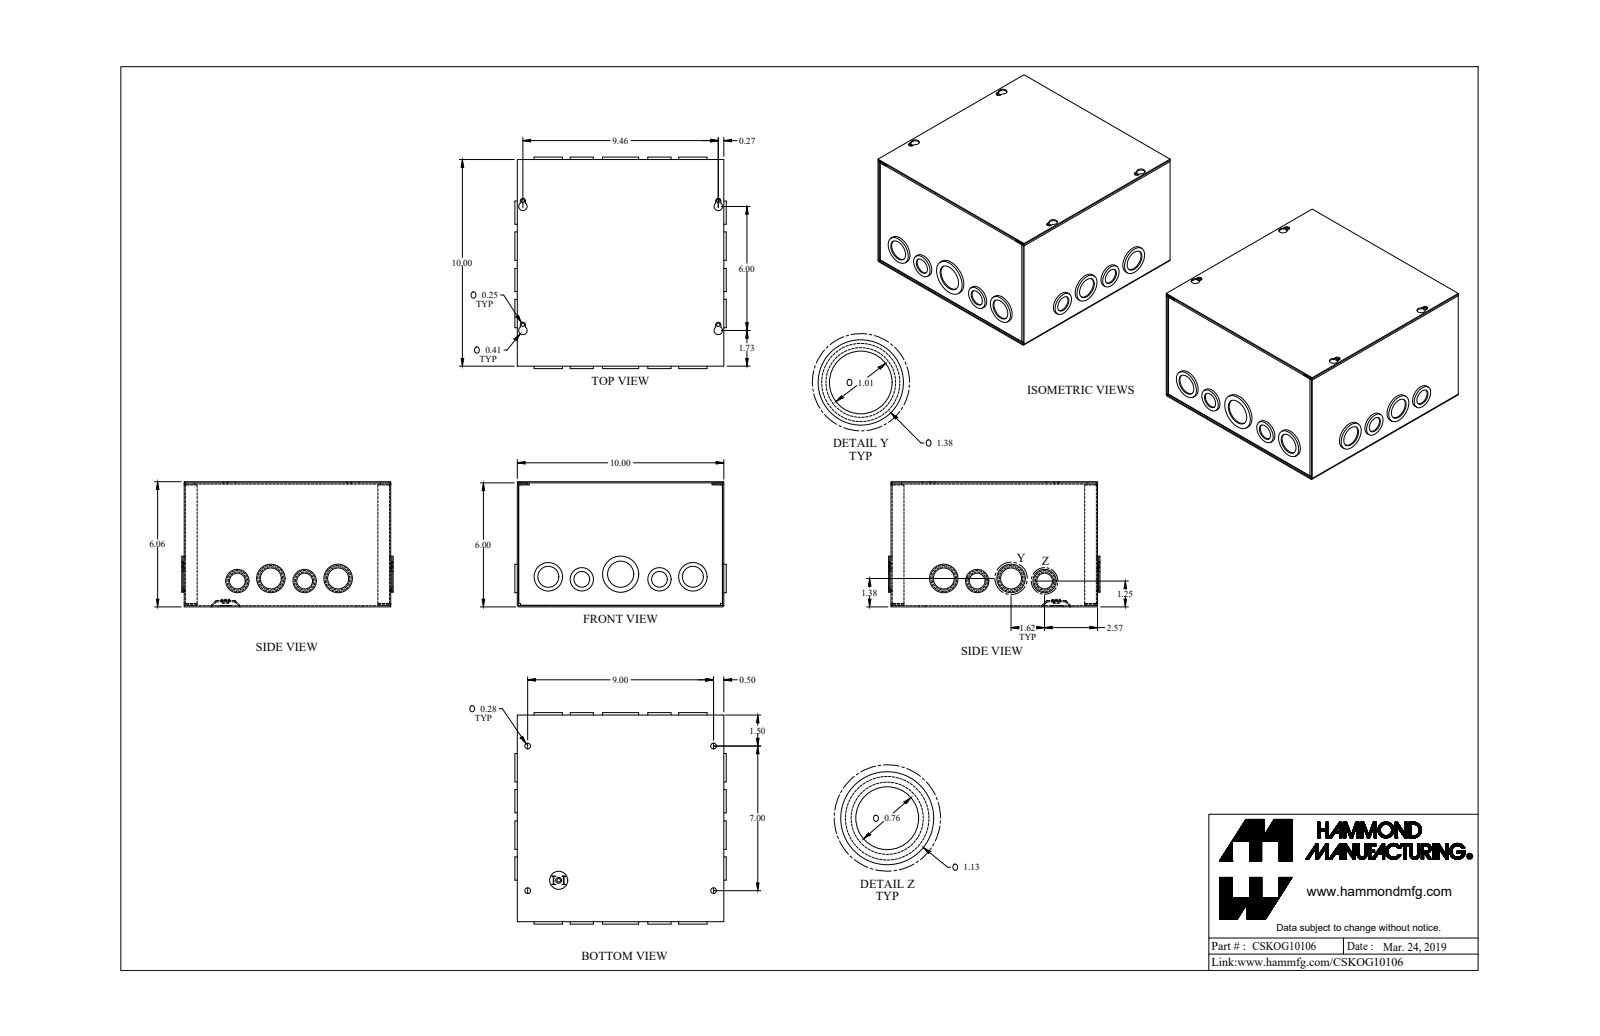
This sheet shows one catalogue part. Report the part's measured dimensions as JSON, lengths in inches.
{"part_name": "CSKOG10106_Default", "step_written_by": "SolidWorks 2019 (CONFIG_CONTROL_DESIGN)", "units": "inches", "bodies": {"solids": 4, "faces": 421, "planar": 197, "cylindrical": 216, "other": 8}, "overall_size": [10.234, 10.234, 6.057], "volume_in3": 27.62, "surface_area_in2": 980.2, "round_holes": [[1.011, 8], [1.261, 6], [0.17, 5], [0.281, 4], [0.761, 4], [0.5, 1], [1.636, 1]], "round_bosses_or_shafts": [[1.375, 5], [1.125, 5], [0.875, 4], [1.375, 3], [1.125, 3], [0.875, 2], [1.75, 1], [0.492, 1]], "partial_cylinders_radius": [[0.029, 12], [0.086, 12], [0.057, 8], [0.125, 4], [0.203, 4]], "face_to_face_distances": [0.057, 9.943, 6, 10, 5.943, 9.886, 6.057, 0.114, 0.07, 9.873], "hole_center_spacings": [1.625, 0.55, 6.504, 9.243, 11.289, 3.26, 7, 1.896]}
